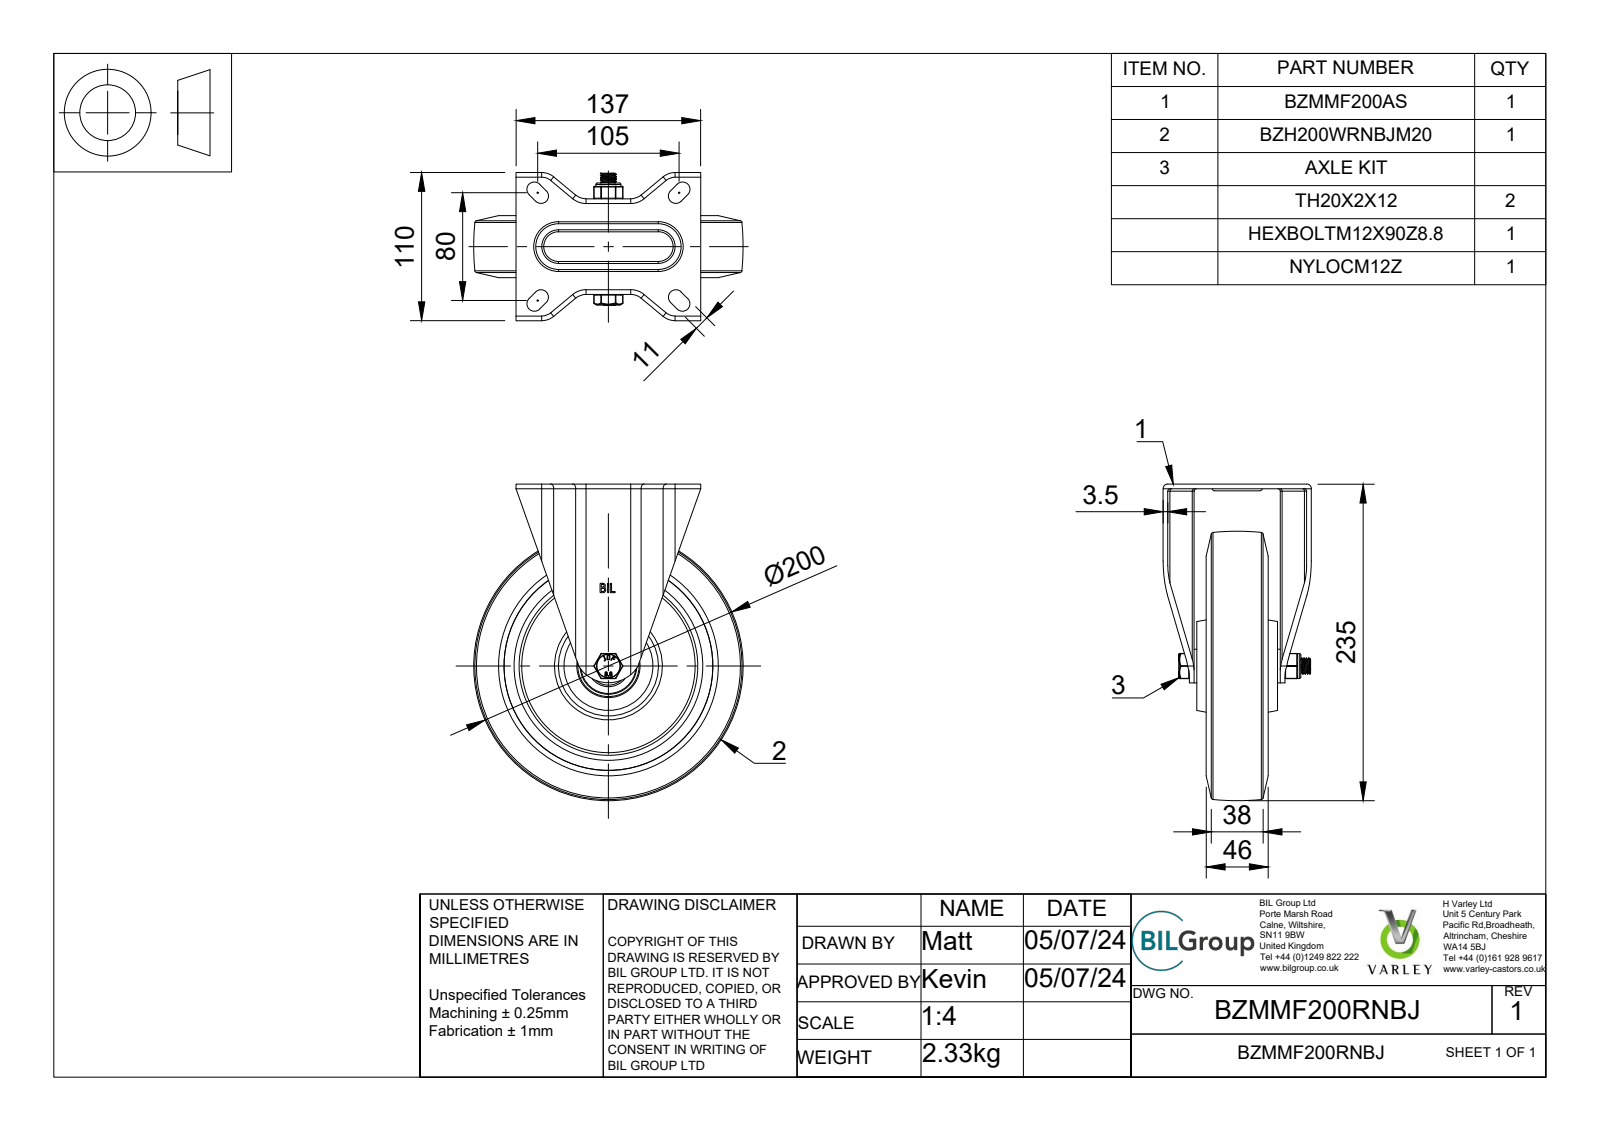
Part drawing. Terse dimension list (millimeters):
name: BZMMF200RNBJ v4; BZMMF200AS - 64 v1; ZINC PLATED, PRESSED STEEL BRACKET; BZH200WRNBJM20 v1 (+7 more)
written by: Autodesk Translation Framework v13.14.0.145 (AUTOMOTIVE_DESIGN)
unit: mm
bodies: 35 solids, 1111 faces (435 planar, 228 cylindrical, 448 other)
size: 235 × 200 × 110
volume: 1 132 000 mm³; area: 289 515 mm²
holes: 1× ⌀12, 1× ⌀12.2, 1× ⌀14, 1× ⌀20, 1× ⌀28.5, 1× ⌀30.8, 1× ⌀40.3, 1× ⌀40.5, 1× ⌀42, 1× ⌀45.5, 1× ⌀47, 1× ⌀155
bosses: 1× ⌀40.8, 1× ⌀31.3, 1× ⌀27, 1× ⌀25, 1× ⌀24, 1× ⌀19.8, 1× ⌀18.5, 1× ⌀17.75
rounds: 19× R0.5, 8× R1.5, 8× R1.75, 8× R3.5, 8× R5.5, 4× R0.47, 4× R0.9, 4× R6
face distances: 3.5, 19, 28, 36, 9, 55, 27, 67.5, 12.5, 39.5
